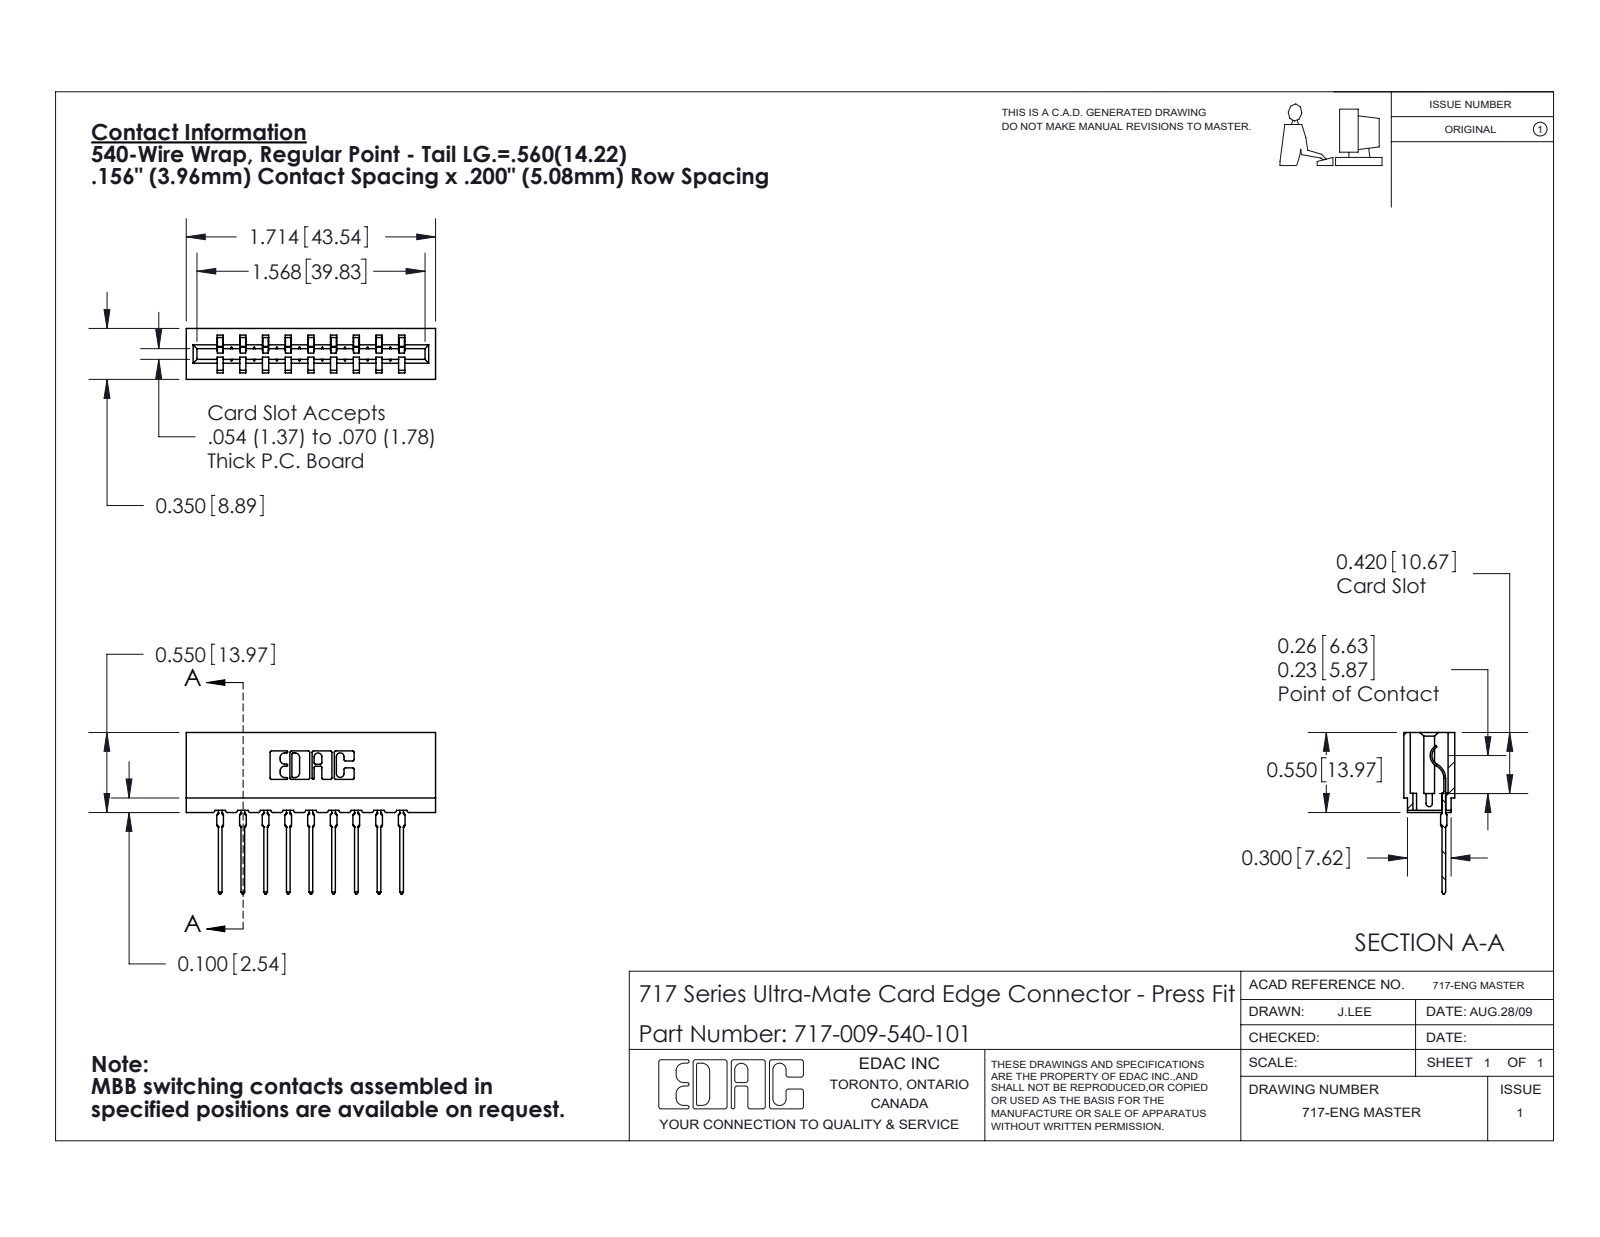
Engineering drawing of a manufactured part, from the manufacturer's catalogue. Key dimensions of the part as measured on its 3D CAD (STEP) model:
Part name (STEP PRODUCT): 717-009-540-101; 745-292-001_540; 717 Part_Insulator Option - 06
STEP written by: SolidWorks 2020 (CONFIG_CONTROL_DESIGN)
Units: inches
Bodies: 10 solids, 1111 faces (666 planar, 211 cylindrical, 234 other)
Overall size (bounding box): 1.714 × 1.109 × 0.35
Volume: 0.235 in³ · Surface area: 7.981 in²
Partial cylindrical surfaces — rounded edges, fillets, slot ends (radius × count): R0.01 ×22, R0.015 ×18, R0.021 ×18, R0.007 ×6, R0.031 ×6, R0.005 ×4, R0.011 ×4, R0.026 ×3
Main face-to-face distances: 0.156, 0.212, 0.624, 0.138, 0.468, 0.198, 0.35, 0.312, 0.042, 0.312
